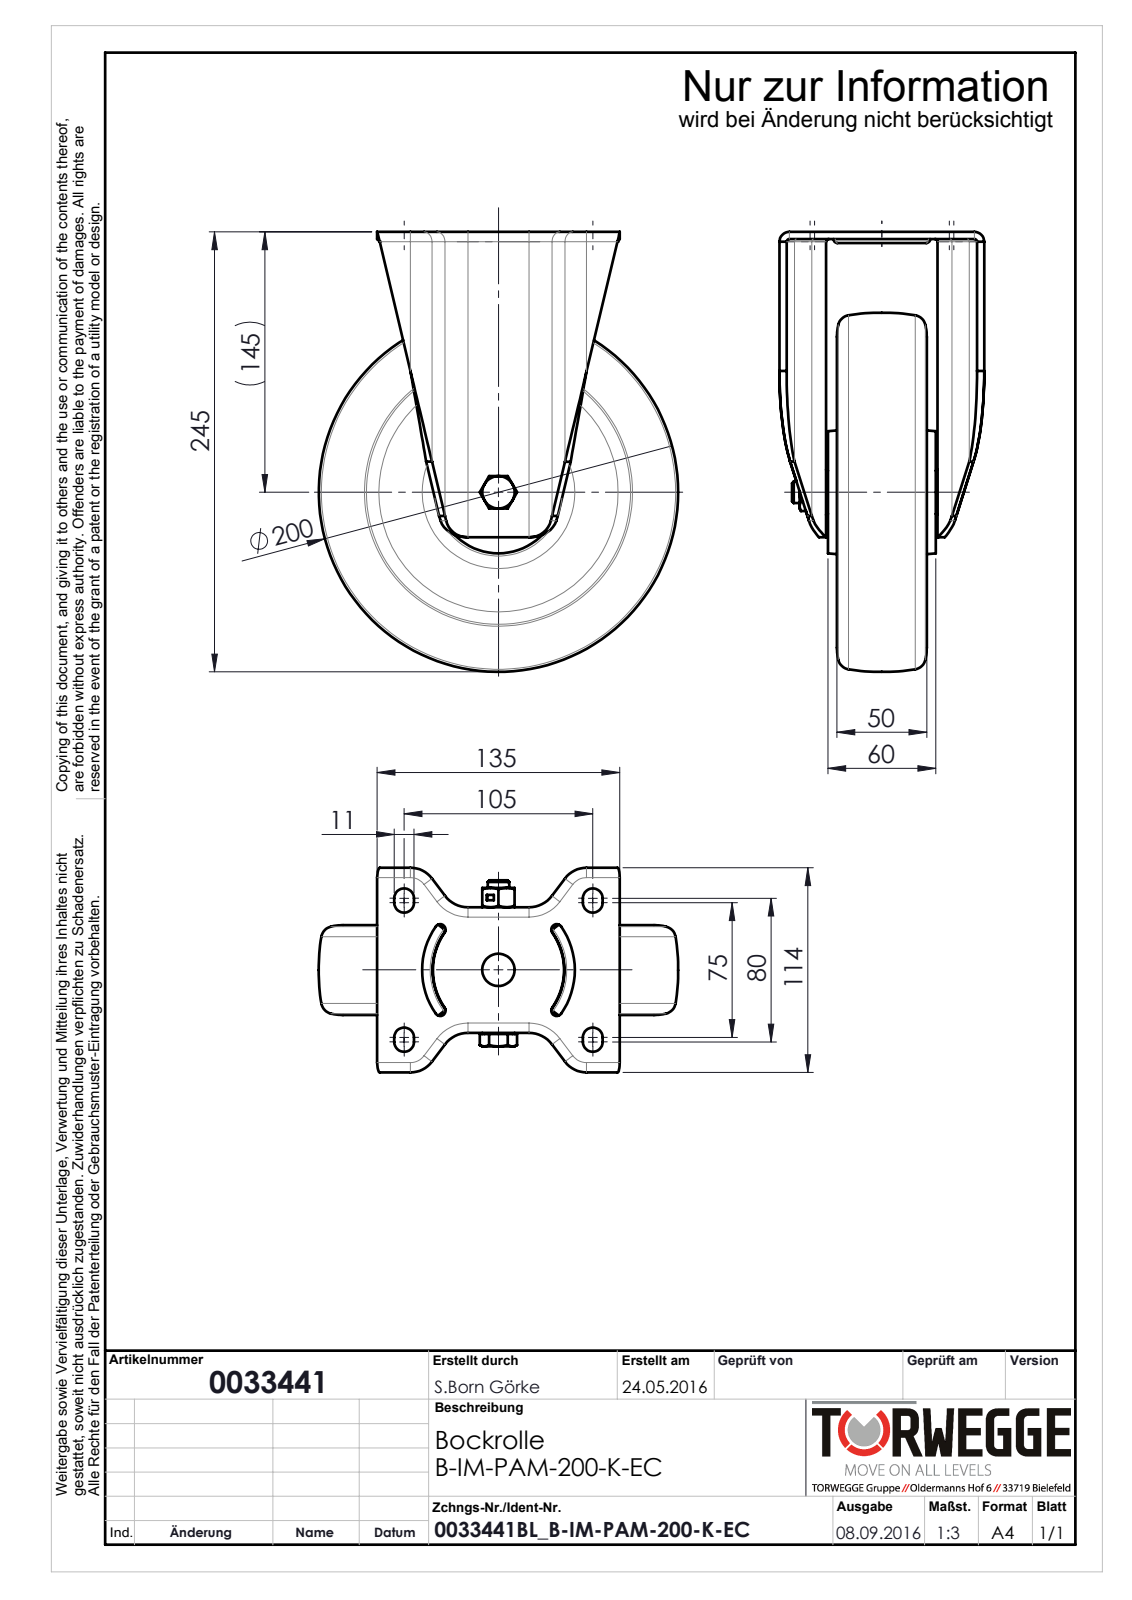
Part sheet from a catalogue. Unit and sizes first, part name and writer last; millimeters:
Units: millimetres
Overall size (bounding box): 245.01 × 200 × 114
Round holes (diameter × count): ⌀10.2 ×1, ⌀12 ×1, ⌀12.2 ×1, ⌀12.5 ×1, ⌀18 ×1, ⌀20 ×1, ⌀20.5 ×1, ⌀35 ×1, ⌀38.9 ×1
Round bosses / shafts (diameter × count): ⌀47 ×1, ⌀28.1 ×1, ⌀25 ×1, ⌀24 ×1, ⌀19.9 ×1, ⌀18 ×1
Partial cylindrical surfaces — rounded edges, fillets, slot ends (radius × count): R5.5 ×16, R1.5 ×8, R2.2 ×4, R3 ×4, R11 ×4, R15 ×4, R16 ×4, R20 ×4
Main face-to-face distances: 4, 40.5, 36.5, 29.5, 66, 25.5, 2, 11, 1, 22
Volume: 1 220 000 mm³ · Surface area: 248 672 mm²
Bodies: 9 solids, 422 faces (124 planar, 132 cylindrical, 166 other)
Part name (STEP PRODUCT): 0033441BL_B-IM-PAM-200-K-EC
STEP written by: SolidWorks 2016 (AUTOMOTIVE_DESIGN)
